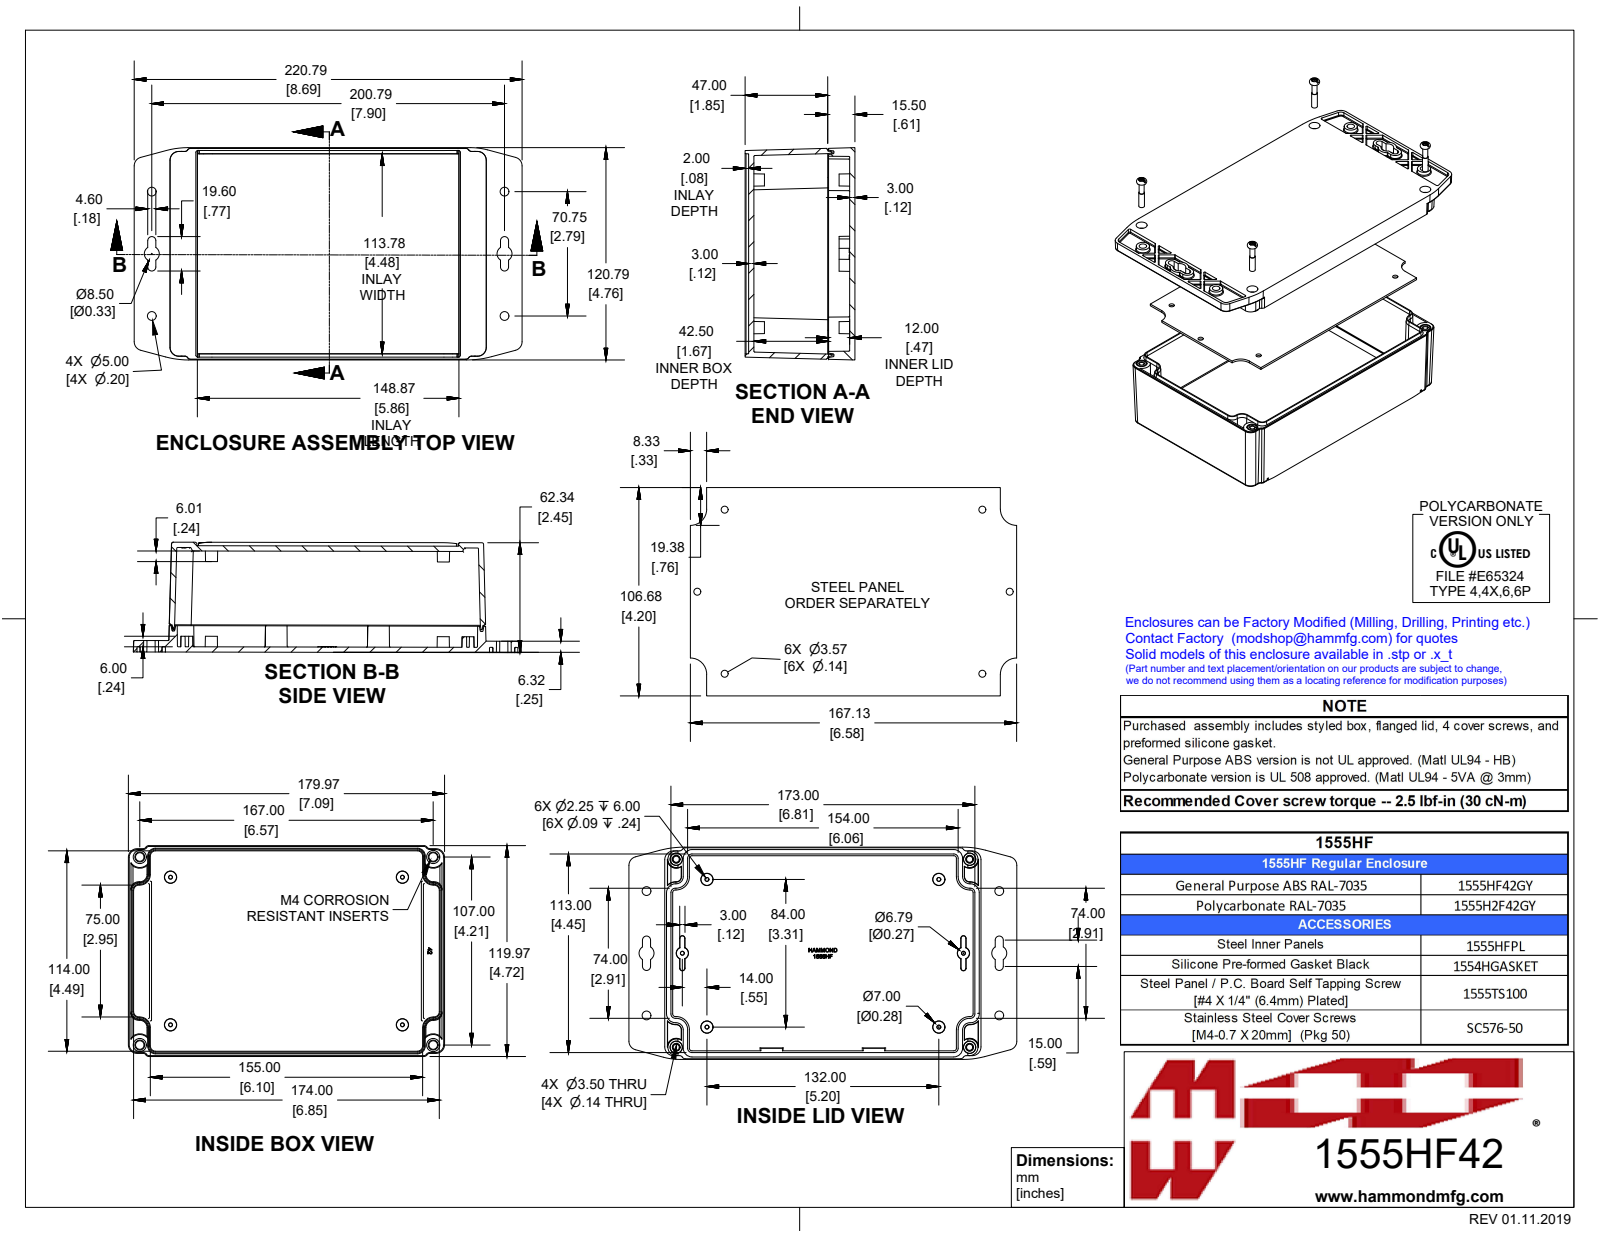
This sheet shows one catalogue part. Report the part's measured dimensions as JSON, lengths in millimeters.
{"part_name": "1555HF42GY", "step_written_by": "SolidWorks 2019 (CONFIG_CONTROL_DESIGN)", "units": "millimeters", "bodies": {"solids": 11, "faces": 1341, "planar": 587, "cylindrical": 297, "other": 457}, "overall_size": [220.8, 120.8, 62.5], "volume_mm3": 298600, "surface_area_mm2": 222100, "round_holes": [[3.6, 6], [3.3, 4], [3.5, 4], [7.5, 4]], "round_bosses_or_shafts": [[9, 4], [6.4, 4], [5.5, 4], [5.3, 4], [3.9, 4], [3.4, 4]], "partial_cylinders_radius": [[0.5, 141], [5, 12], [1, 10], [2.3, 4], [3.5, 4], [4.3, 4], [4.7, 4], [8.3, 4]], "face_to_face_distances": [3, 57.5, 6, 9, 48.5, 60.5, 10.4, 7.4, 1.4, 51.5], "hole_center_spacings": [20.9, 44.3, 53.6, 97.1, 149.9, 151.9, 172, 177.4]}
